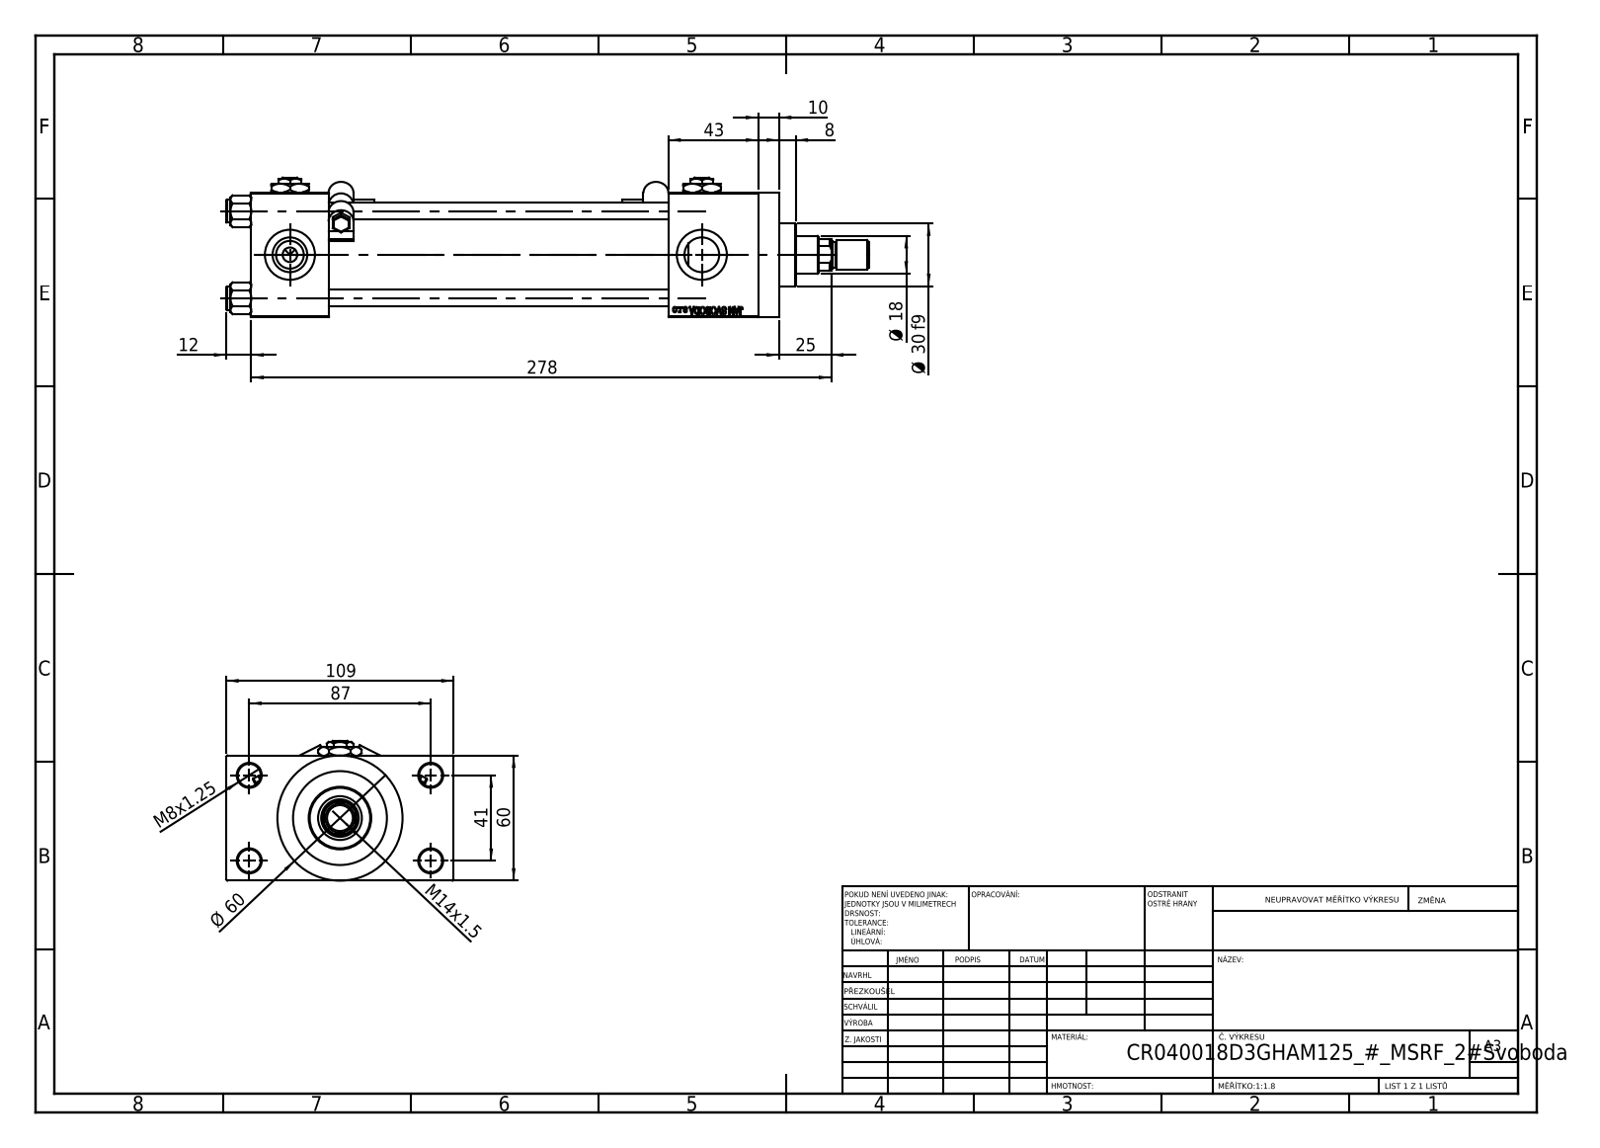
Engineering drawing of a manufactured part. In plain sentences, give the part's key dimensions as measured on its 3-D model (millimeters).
The part is named "NUT_M5_D; V215_VC_A; V215CR_D_Body; MSRF_MSRG1 (+4 more)". Its 3-D file was written by "SolidWorks 2019 (CONFIG_CONTROL_DESIGN)". It is 16 solids with 1283 faces: 586 planar, 131 cylindrical and 566 other. Overall it measures 308 by 109 by 67 millimeters. Its volume is 610 467 cubic millimeters and its surface area 175 473 square millimeters. Round holes: 4 of diameter 8, 4 of diameter 11, 4 of diameter 16.66, 4 of diameter 24, 3 of diameter 7, 1 of diameter 8.5, 1 of diameter 18, 1 of diameter 21, 1 of diameter 31, 1 of diameter 40, 1 of diameter 45. Round bosses or shafts: 4 of diameter 11, 2 of diameter 5, 2 of diameter 2.5, 1 of diameter 60, 1 of diameter 46, 1 of diameter 30, 1 of diameter 14, 1 of diameter 12. Partial cylindrical surfaces (rounded edges, fillets, slot ends): 12 of radius 0.5, 4 of radius 6, 1 of radius 8.5. The main face-to-face distances are 60, 163, 24.5, 200, 84.5, 37, 43, 243, 206, 53. The hole center spacings are 22.65, 29.49, 41.7, 47.15, 48.09, 64.35, 76.49, 41.
